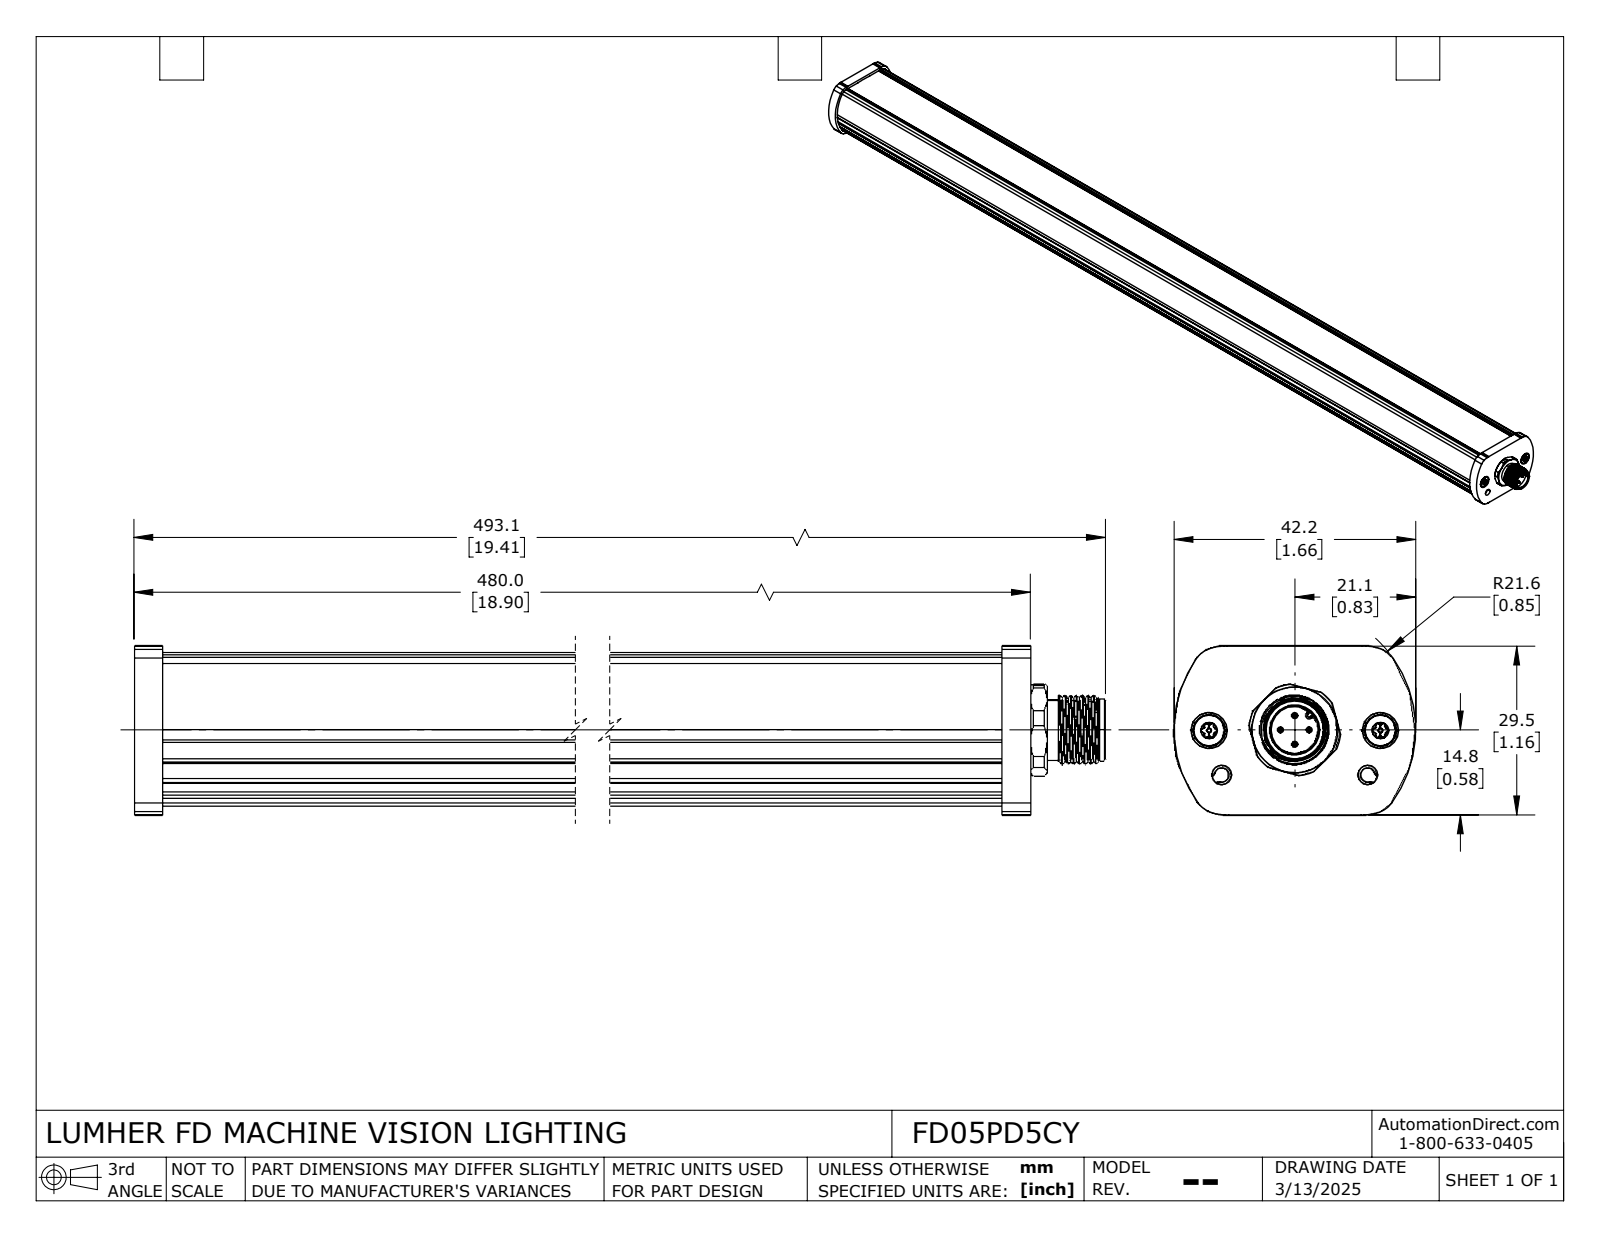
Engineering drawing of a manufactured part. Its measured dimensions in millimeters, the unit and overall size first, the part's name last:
Units: millimetres
Overall size (bounding box): 493.1 × 42.21 × 29.45
Round holes (diameter × count): ⌀1.45 ×4, ⌀3.4 ×4, ⌀8.3 ×1, ⌀9 ×1, ⌀9.4 ×1
Round bosses / shafts (diameter × count): ⌀1.4 ×4, ⌀1 ×4, ⌀5.6 ×2, ⌀3 ×2, ⌀0.8 ×2, ⌀11.9 ×1, ⌀10.6 ×1, ⌀10.5 ×1
Partial cylindrical surfaces — rounded edges, fillets, slot ends (radius × count): R0.57 ×24, R0.25 ×12, R0.8 ×12, R3 ×10, R0.3 ×4, R1.25 ×4, R3.1 ×4, R4.6 ×4
Main face-to-face distances: 2.5, 5, 7.5, 10, 12.5, 4, 15, 2, 17.5, 3
Hole centre spacings: 2.5, 3.54, 14.96, 5, 8.06, 12.46, 12.91, 13.83
Volume: 407 393 mm³ · Surface area: 100 958 mm²
Bodies: 1 solid, 662 faces (97 planar, 383 cylindrical, 182 other)
Part name (STEP PRODUCT): FD05PD5CY
STEP written by: SolidWorks 2024 (AUTOMOTIVE_DESIGN)
